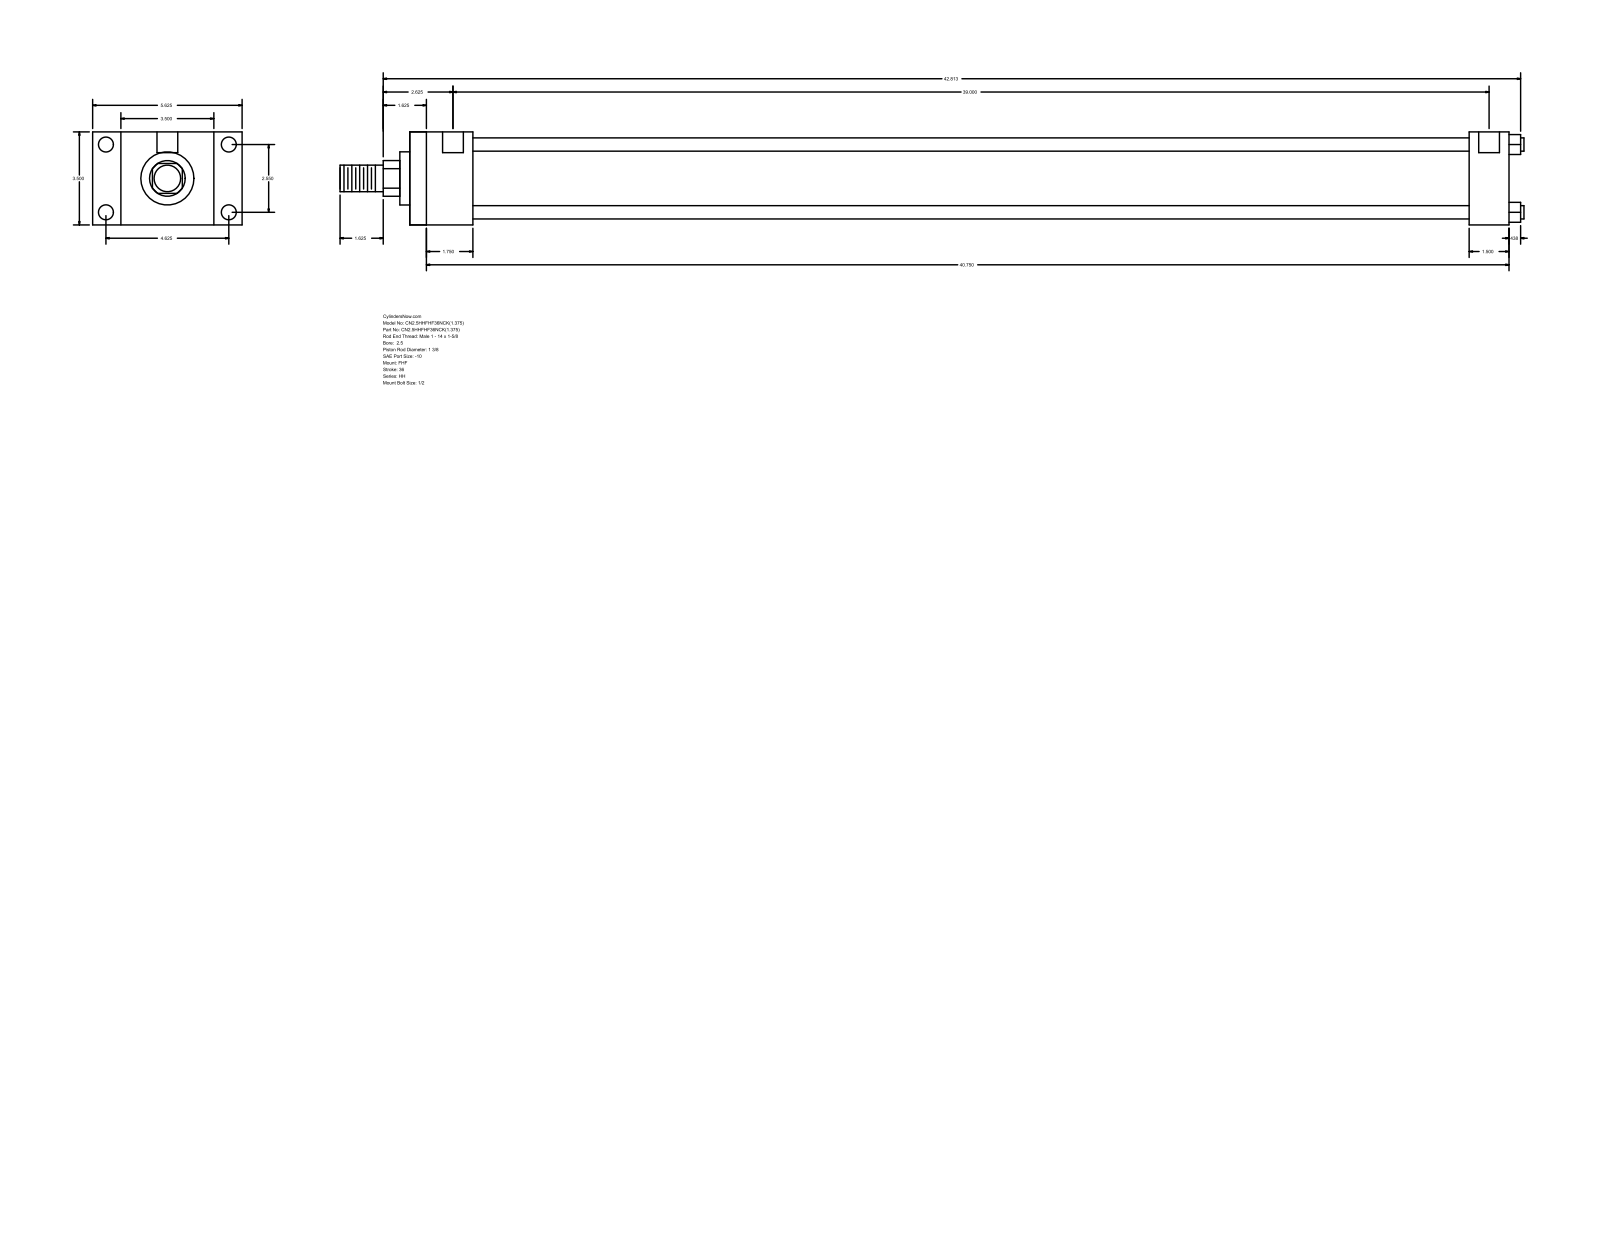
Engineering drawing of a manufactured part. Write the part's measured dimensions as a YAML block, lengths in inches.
part_name: "HH_FHF__0250_1.375"
step_written_by: "GSSL Pune (CONFIG_CONTROL_DESIGN)"
units: inches
bodies: {solids: 0, faces: 88, planar: 60, cylindrical: 28, other: 0}
overall_size: [44.563, 5.625, 3.5]
round_holes:
  - {diameter: 0.219, count: 4}
  - {diameter: 0.563, count: 4}
  - {diameter: 0.781, count: 2}
round_bosses_or_shafts:
  - {diameter: 0.5, count: 4}
  - {diameter: 2.875, count: 1}
  - {diameter: 2, count: 1}
  - {diameter: 1.375, count: 1}
  - {diameter: 1, count: 1}
partial_cylinders:
  - {radius: 0.672, count: 1}
face_to_face_distances: [3.5, 2.375, 1.063, 4.563, 41.375, 39, 5.625, 39.875, 37.5, 1.5]
hole_center_spacings: [0.062, 2.55, 4.625, 5.281, 39.063, 39.125, 39]
